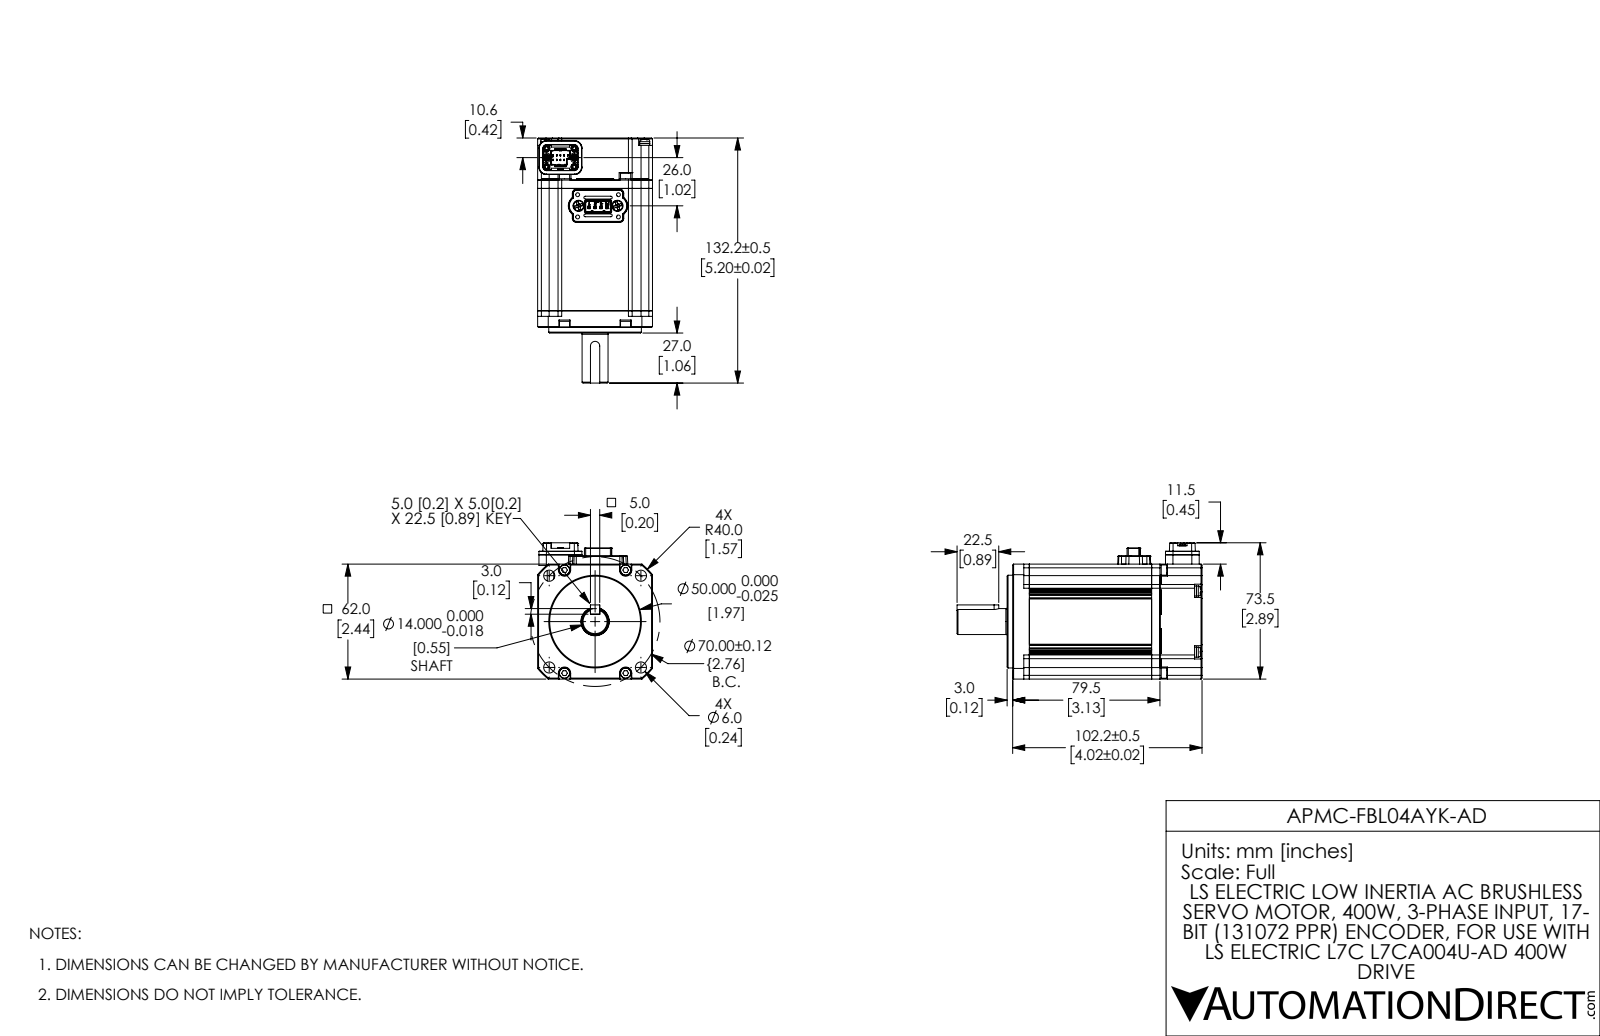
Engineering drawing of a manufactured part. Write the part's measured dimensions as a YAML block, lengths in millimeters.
part_name: "APMC-FBL04AYK-AD"
step_written_by: "SolidWorks 2017 (AUTOMOTIVE_DESIGN)"
units: millimeters
bodies: {solids: 45, faces: 1851, planar: 1196, cylindrical: 478, other: 177}
overall_size: [132.2, 73.5, 62]
volume: 358900
surface_area: 75610
round_holes:
  - {diameter: 2.1, count: 10}
  - {diameter: 3, count: 10}
  - {diameter: 3.5, count: 8}
  - {diameter: 1.6, count: 6}
  - {diameter: 6, count: 6}
  - {diameter: 3.1, count: 4}
  - {diameter: 3.3, count: 1}
  - {diameter: 3.4, count: 1}
  - {diameter: 15.3, count: 1}
round_bosses_or_shafts:
  - {diameter: 5.4, count: 6}
  - {diameter: 5.6, count: 4}
  - {diameter: 5.5, count: 4}
  - {diameter: 2.2, count: 2}
  - {diameter: 50, count: 1}
  - {diameter: 15, count: 1}
  - {diameter: 14.8, count: 1}
  - {diameter: 14, count: 1}
partial_cylinders:
  - {radius: 0.2, count: 20}
  - {radius: 0.3, count: 20}
  - {radius: 3, count: 12}
  - {radius: 1, count: 10}
  - {radius: 0.2, count: 9}
  - {radius: 2, count: 8}
  - {radius: 0.5, count: 7}
  - {radius: 0.1, count: 6}
face_to_face_distances: [4.5, 62, 0.7, 5.2, 66, 70.5, 71.2, 11, 51, 9]
hole_center_spacings: [5, 6, 8.5, 8.8, 15.3, 16, 22.3, 31.5]
